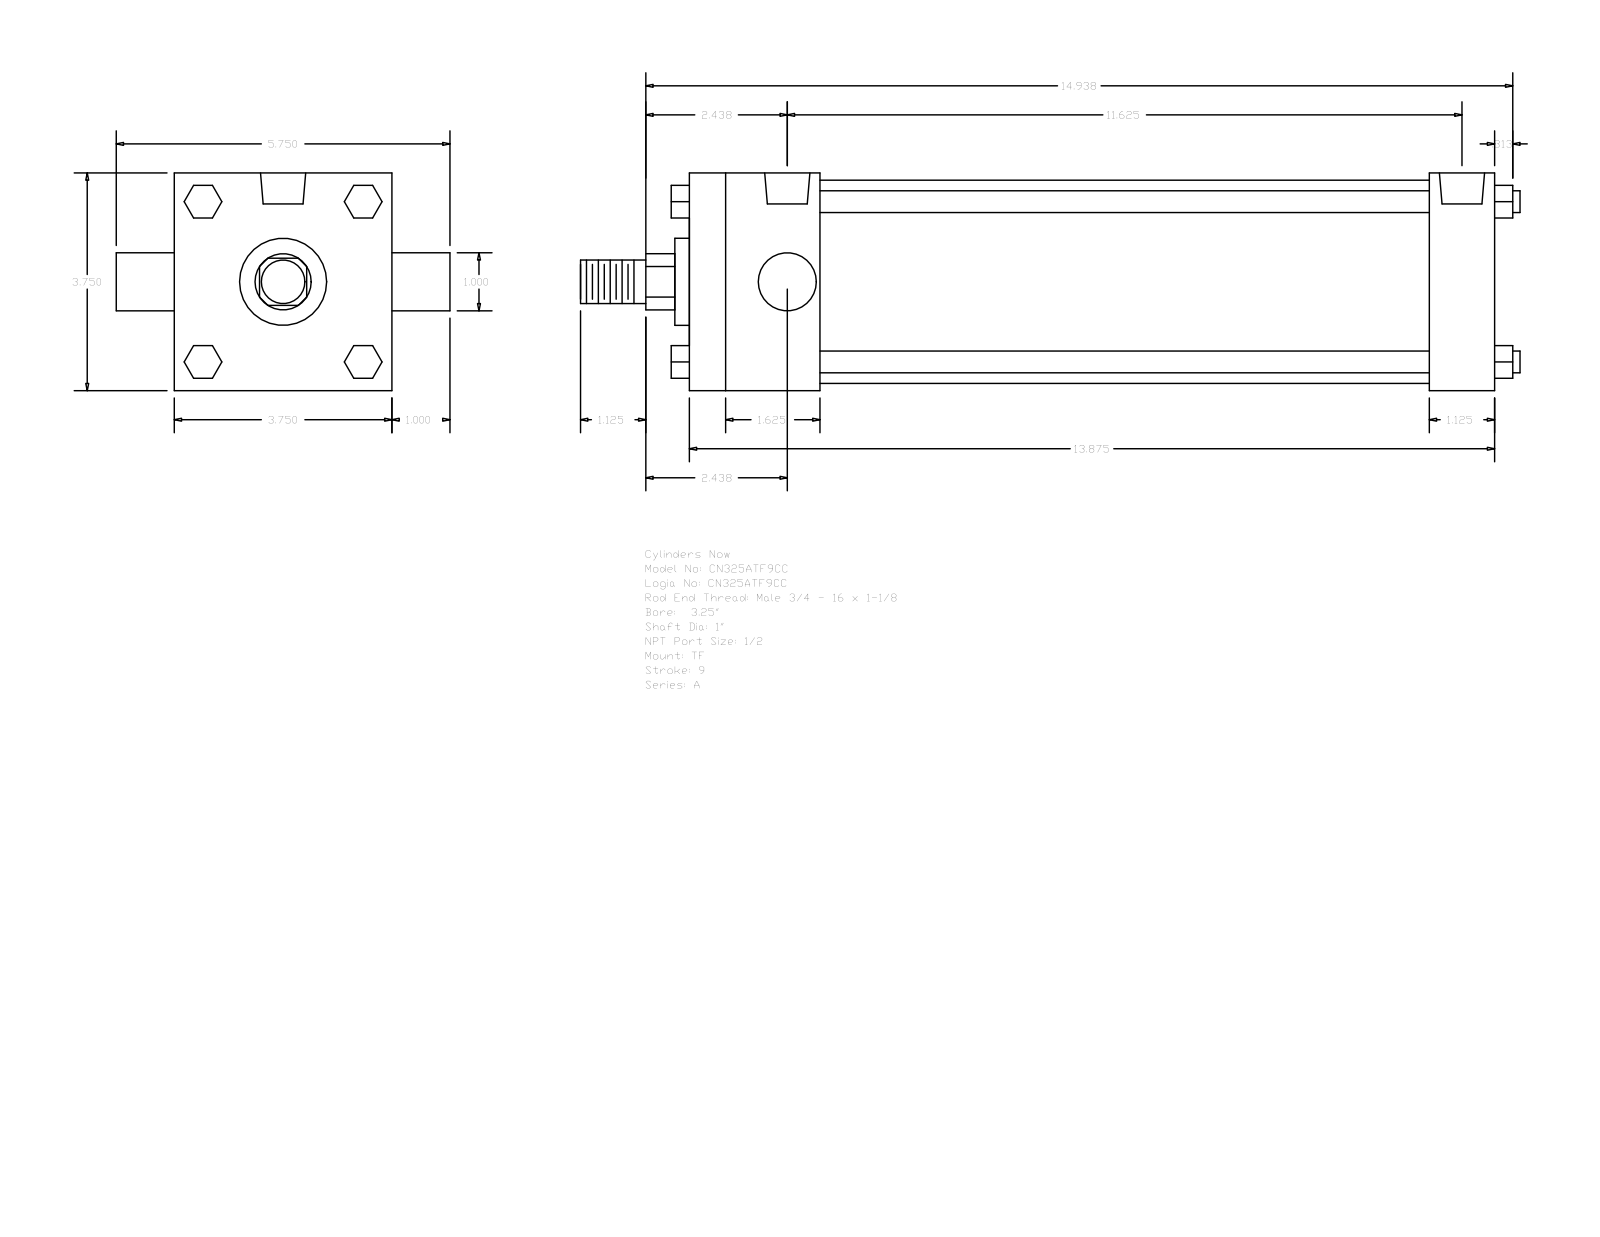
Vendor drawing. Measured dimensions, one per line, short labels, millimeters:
name: A_TF__0325_1
written by: GSSL Pune (CONFIG_CONTROL_DESIGN)
unit: mm
bodies: 0 solids, 120 faces (92 planar, 28 cylindrical, 0 other)
size: 411.16 × 146.05 × 95.25
holes: 3× ⌀8.73, 2× ⌀19.77
bosses: 4× ⌀9.53, 2× ⌀25.4, 1× ⌀88.9, 1× ⌀38.1, 1× ⌀19.05
rounds: 1× R12.29
face distances: 95.24, 352.43, 57.15, 323.85, 266.7, 295.28, 28.58, 14.28, 35.05, 60.71
hole spacings: 3.18, 292.1, 288.92, 295.28
